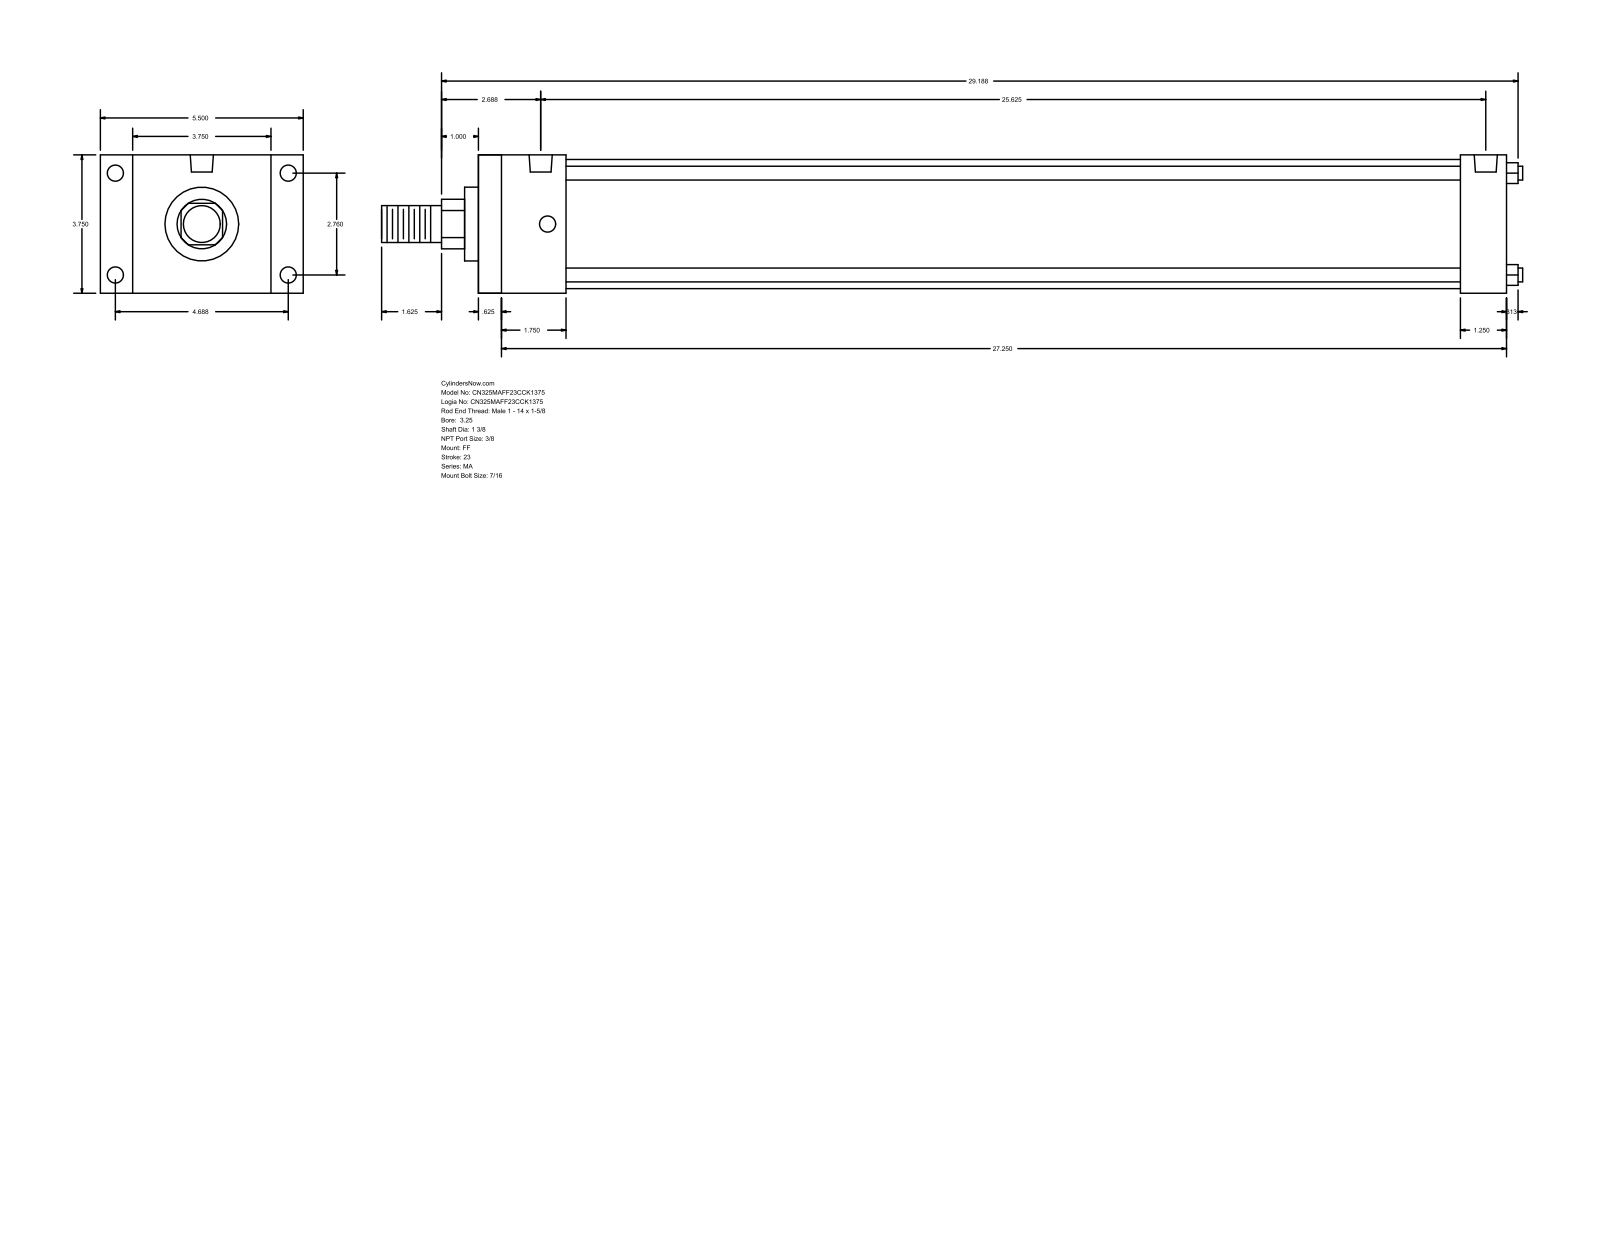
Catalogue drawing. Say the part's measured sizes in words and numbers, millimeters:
The part is named "MA_FF__0325_1.375". Its 3-D file was written by "GSSL Pune (CONFIG_CONTROL_DESIGN)". It is 0 solids with 92 faces: 64 planar, 28 cylindrical and 0 other. Overall it measures 785.81 by 139.7 by 95.25 millimeters. Round holes: 8 of diameter 11.11, 2 of diameter 15.93. Round bosses or shafts: 4 of diameter 9.53, 1 of diameter 88.9, 1 of diameter 50.8, 1 of diameter 34.92, 1 of diameter 25.4. Partial cylindrical surfaces (rounded edges, fillets, slot ends): 1 of radius 17.06. The main face-to-face distances are 95.24, 708.02, 15.87, 692.15, 22.23, 117.47, 60.32, 676.27, 44.45, 660.4. The hole center spacings are 70.1, 119.06, 138.16, 641.35, 4.76, 4.77, 646.11, 646.12.
